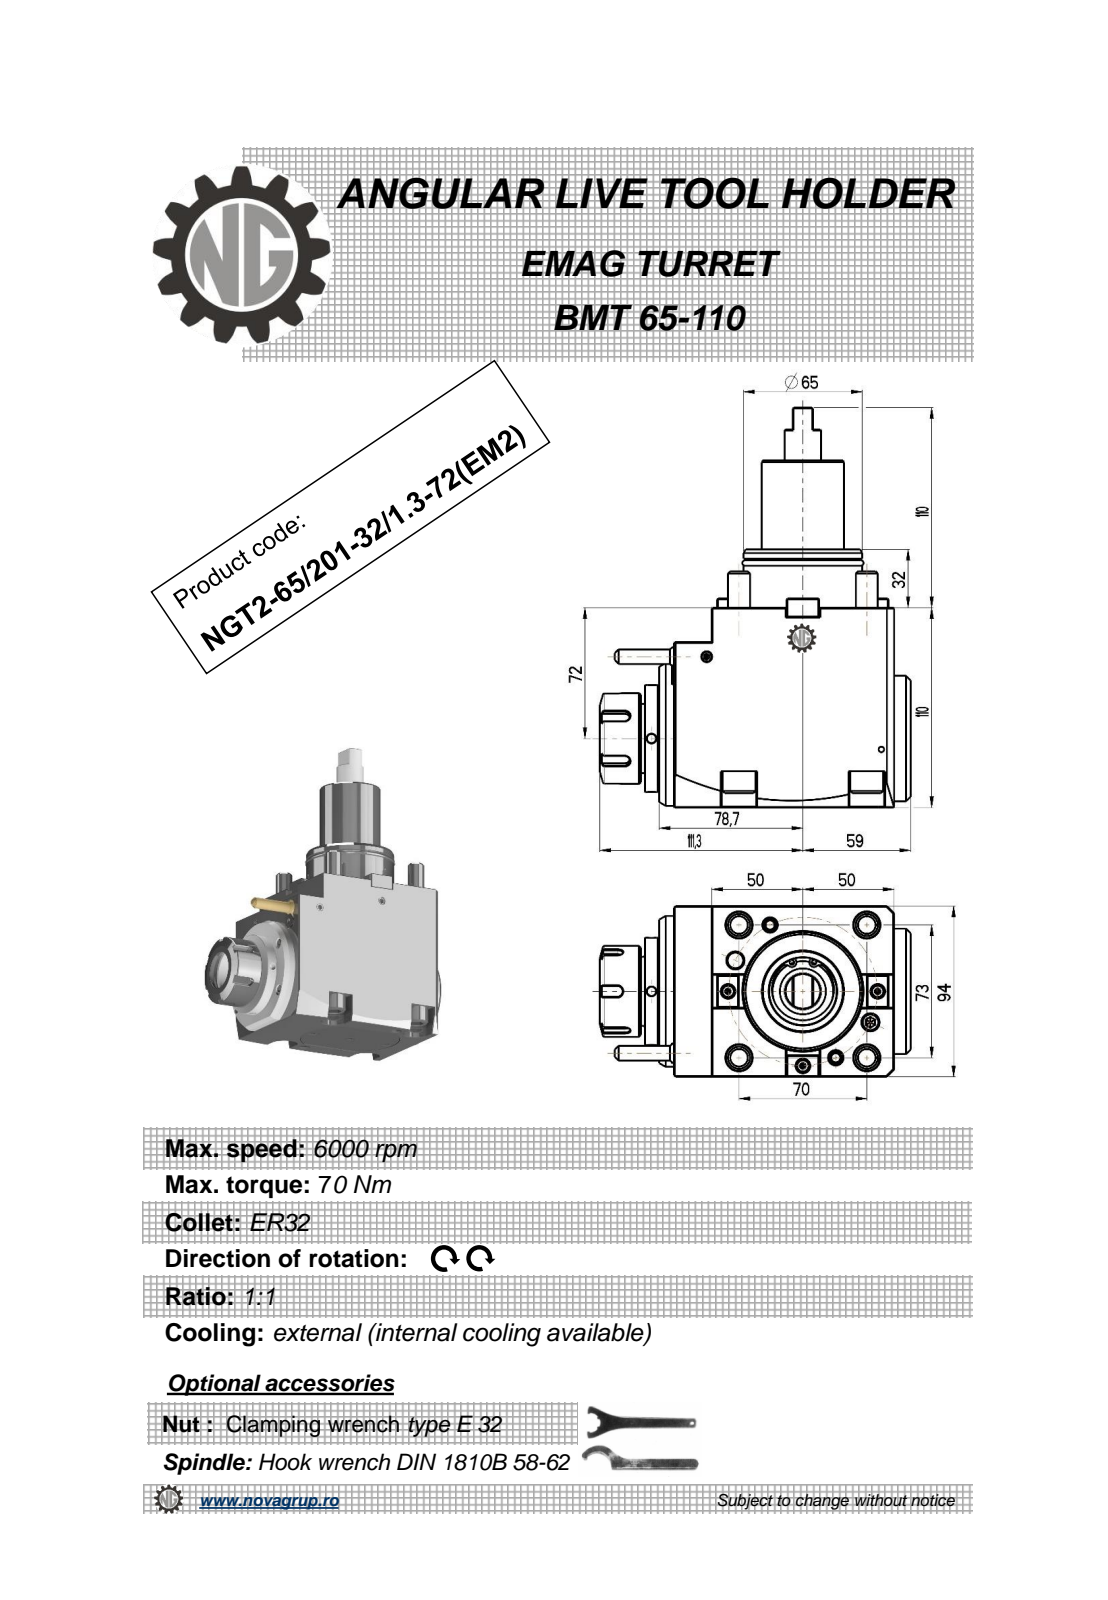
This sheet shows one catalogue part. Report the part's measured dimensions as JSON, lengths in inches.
{"part_name": "NGT2_65_201_32_1_3_72_EM2", "step_written_by": "PRO/ENGINEER BY PARAMETRIC TECHNOLOGY CORPORATION, 2010280 (CONFIG_CONTROL_DESIGN)", "units": "inches", "bodies": {"solids": 2, "faces": 442, "planar": 216, "cylindrical": 110, "other": 116}, "overall_size": [8.661, 6.705, 3.701], "volume_in3": 93.37, "surface_area_in2": 171.5, "round_holes": [[0.197, 3], [0.335, 2], [0.118, 1], [1.063, 1]], "round_bosses_or_shafts": [[0.709, 4], [0.472, 4], [3.268, 1], [2.717, 1], [2.559, 1], [2.362, 1], [2.323, 1], [1.969, 1]], "partial_cylinders_radius": [[0.014, 20], [0.009, 6], [0.118, 5], [0.374, 4], [0.031, 2], [21.654, 2]], "face_to_face_distances": [3.701, 4.331, 0.315, 0.354, 5.067, 5.421, 3.937, 4.752, 5.106, 0.748], "hole_center_spacings": [1.929, 2.22, 3.206, 4.77]}
